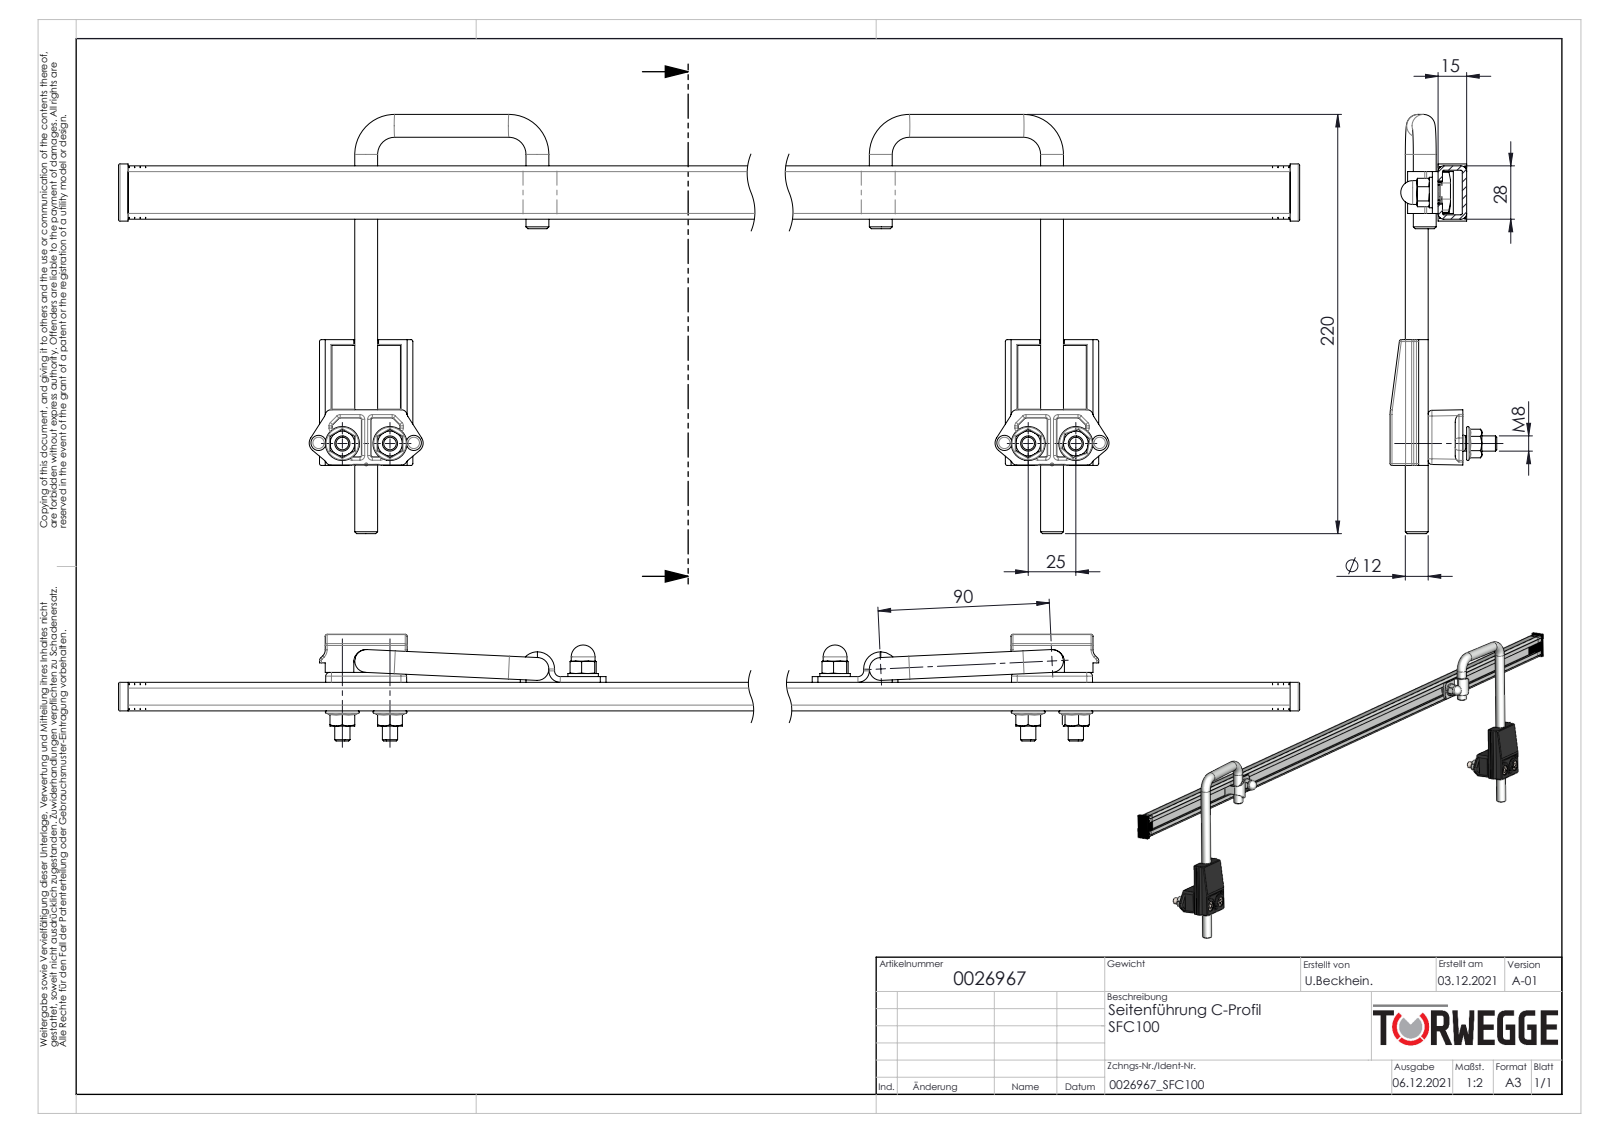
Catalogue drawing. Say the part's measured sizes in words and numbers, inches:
The part is named "0026967". Its 3-D file was written by "SolidWorks 2020 (AUTOMOTIVE_DESIGN)". It is 25 solids with 1212 faces: 458 planar, 350 cylindrical and 404 other. Overall it measures 39.764 by 8.661 by 2.205 inches. Its volume is 21.17 cubic inches and its surface area 350.5 square inches. Round holes: 6 of diameter 0.331, 4 of diameter 0.157, 4 of diameter 0.268, 4 of diameter 0.315, 4 of diameter 0.512, 2 of diameter 0.262, 2 of diameter 0.354. Round bosses or shafts: 6 of diameter 0.472, 6 of diameter 0.315, 2 of diameter 0.63, 2 of diameter 0.492. Partial cylindrical surfaces (rounded edges, fillets, slot ends): 73 of radius 0.039, 30 of radius 0.079, 27 of radius 0.02, 22 of radius 0.059, 10 of radius 0.118, 8 of radius 0.03, 8 of radius 0.374, 4 of radius 0.029. The main face-to-face distances are 0.091, 0.5, 1.012, 0.591, 0.409, 0.921, 1.102, 0.787, 0.315, 0.224. The hole center spacings are 0.984, 6.544, 7.187, 25.093, 26.057, 29.528, 20.559, 28.543.
